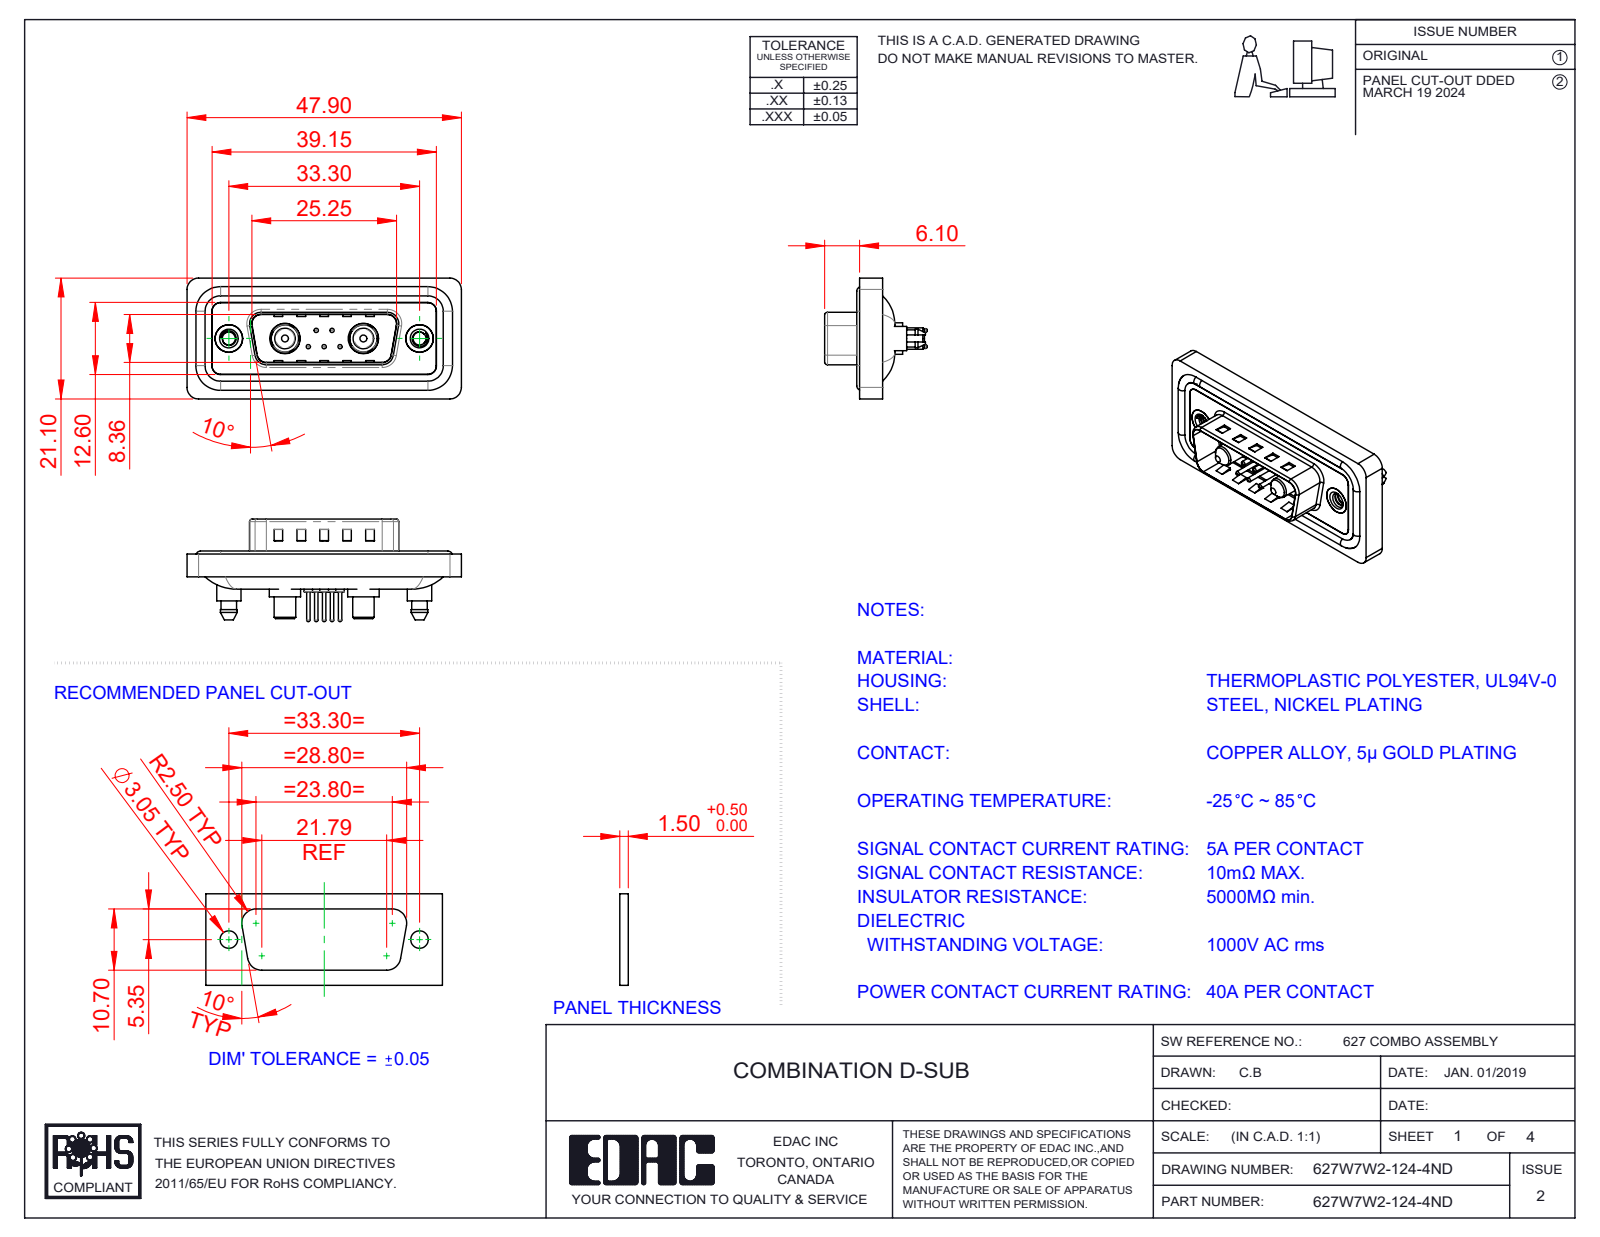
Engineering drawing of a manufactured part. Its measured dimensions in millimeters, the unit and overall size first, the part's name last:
Units: millimetres
Overall size (bounding box): 47.9 × 21.1 × 17.9
Round holes (diameter × count): ⌀0.75 ×5, ⌀1.6 ×5, ⌀2 ×5, ⌀2.26 ×2, ⌀4 ×2, ⌀4.8 ×2, ⌀4.85 ×2, ⌀5 ×2, ⌀5.3 ×2
Round bosses / shafts (diameter × count): ⌀1.5 ×5, ⌀0.6 ×5, ⌀1.6 ×4, ⌀5.5 ×2, ⌀5.4 ×2, ⌀5.2 ×2, ⌀4.9 ×2, ⌀4.75 ×2
Partial cylindrical surfaces — rounded edges, fillets, slot ends (radius × count): R1.5 ×28, R2 ×20, R1.6 ×10, R0.5 ×8, R0.25 ×4, R0.6 ×4, R0.65 ×4, R0.9 ×4
Main face-to-face distances: 0.4, 1.1, 1.6, 1.5, 3.1, 0.5, 2.9, 0.7, 0.82, 9.58
Hole centre spacings: 3.16, 2.77, 9.8, 23.5, 4.31, 4.33, 5.03, 5.04
Volume: 5 688 mm³ · Surface area: 9 151 mm²
Bodies: 16 solids, 768 faces (248 planar, 332 cylindrical, 188 other)
Part name (STEP PRODUCT): 627Combo Shell Front_15 Contacts; 627Combo Threaded Boardlock_D; 627Combo Contact Row 1_24; 627Combo Waterproof Housing_15 Contacts (+6 more)
STEP written by: SolidWorks 2023 (CONFIG_CONTROL_DESIGN)
